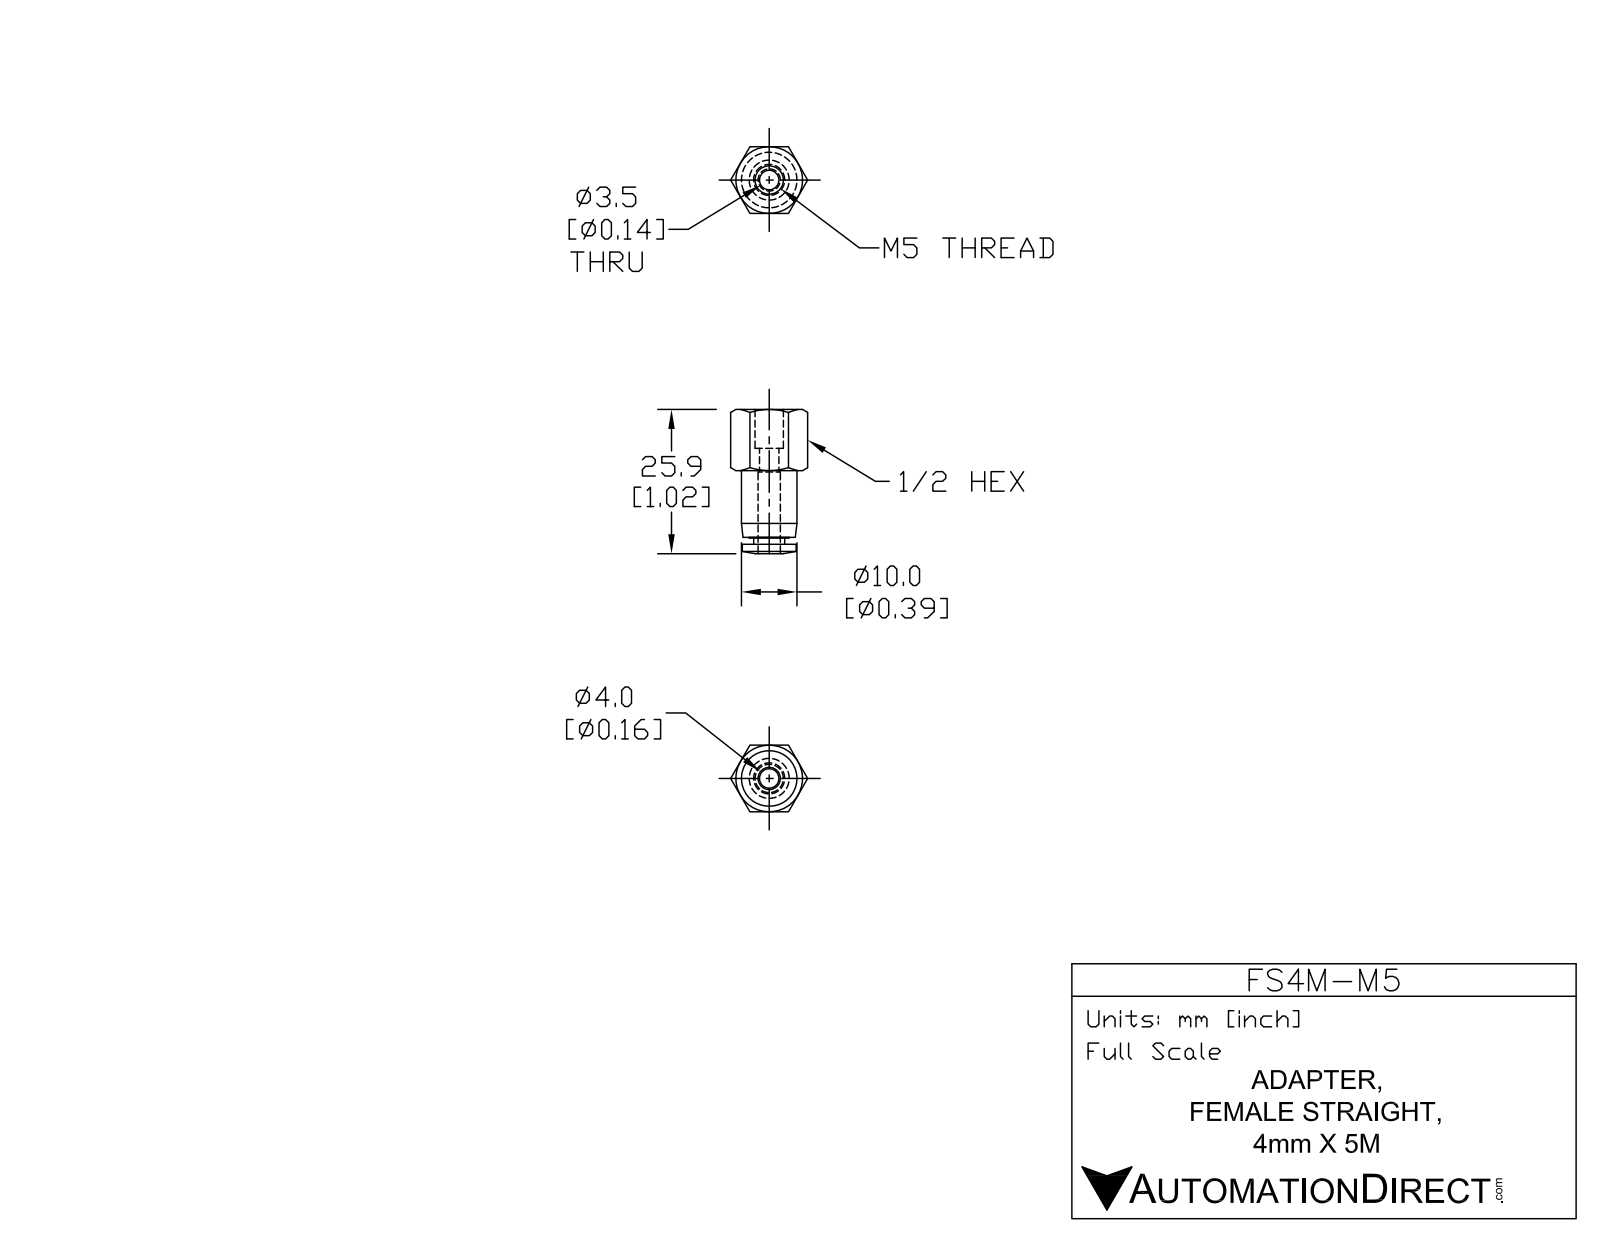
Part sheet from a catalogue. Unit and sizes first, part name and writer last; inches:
Units: inches
Overall size (bounding box): 1.022 × 0.546 × 0.472
Round holes (diameter × count): ⌀0.138 ×1, ⌀0.169 ×1, ⌀0.197 ×1
Round bosses / shafts (diameter × count): ⌀0.394 ×1, ⌀0.382 ×1, ⌀0.283 ×1, ⌀0.22 ×1
Main face-to-face distances: 0.472, 0.955, 0.433, 0.522, 0.906, 0.049, 0.911, 0.478, 0.043, 0.276
Volume: 0.125 in³ · Surface area: 2.413 in²
Bodies: 1 solid, 48 faces (14 planar, 14 cylindrical, 20 other)
Part name (STEP PRODUCT): FS4M-M5
STEP written by: SolidWorks 2015 (AUTOMOTIVE_DESIGN)
